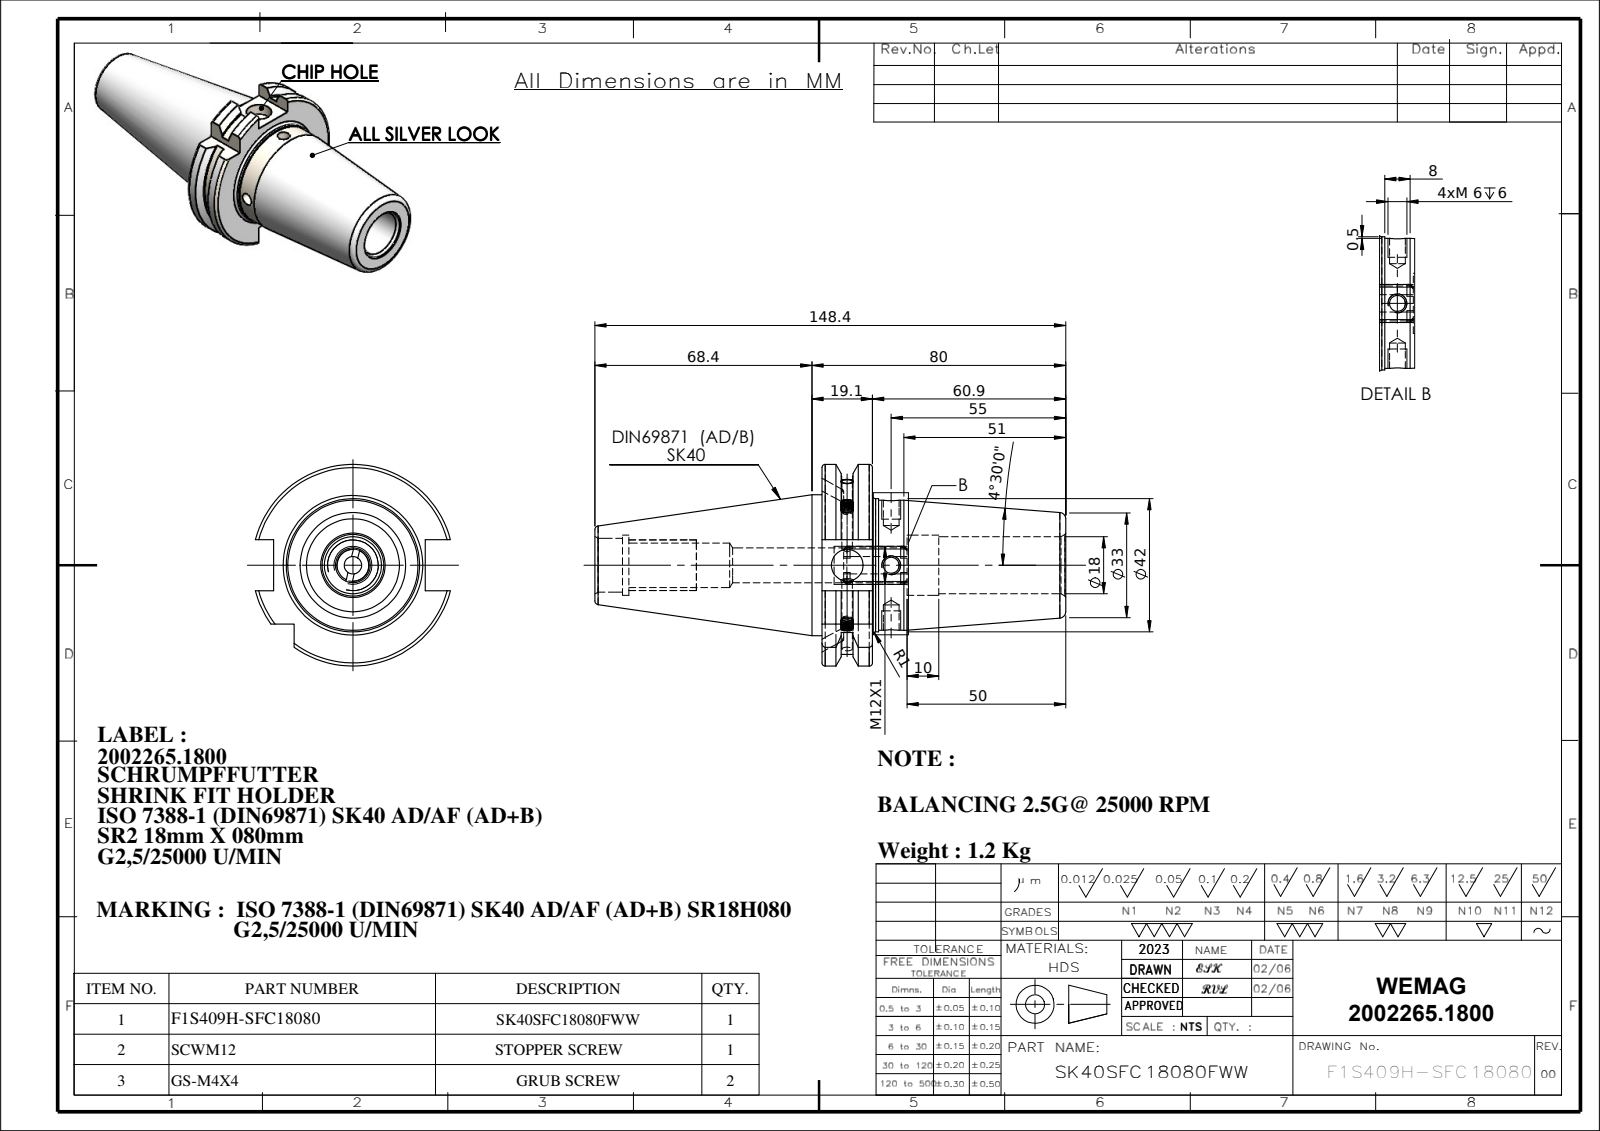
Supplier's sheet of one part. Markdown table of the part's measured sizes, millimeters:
| quantity | value |
| --- | --- |
| part name | GS-M4X4_DIN 913 - M4 x 4-N; SK40SFC18080FWW; SCWM12; 91406-SR21808 |
| STEP written by | SolidWorks 2018 (CONFIG_CONTROL_DESIGN) |
| units | millimeters |
| bodies | 4 solids, 240 faces (66 planar, 68 cylindrical, 106 other) |
| overall size | 148.4 × 63.55 × 61.48 |
| volume | 156 176 mm³ |
| surface area | 32 814 mm² |
| round holes (diameter × count) | 5 × 2, 3.3 × 1, 5.5 × 1, 10 × 1, 11 × 1, 14 × 1, 17 × 1, 17.99 × 1, 18.99 × 1, 19 × 1 |
| round bosses / shafts (diameter × count) | 4 × 2, 44.45 × 1, 42 × 1, 41 × 1, 12 × 1 |
| partial cylindrical surfaces (radius × count) | 28.12 × 1, 31.77 × 1 |
| main face-to-face distances | 15.9, 60.9, 76.8, 26.8, 10.9, 50, 16.1, 47.8, 1.9, 87.7 |
| hole center spacings | 13.85 |
